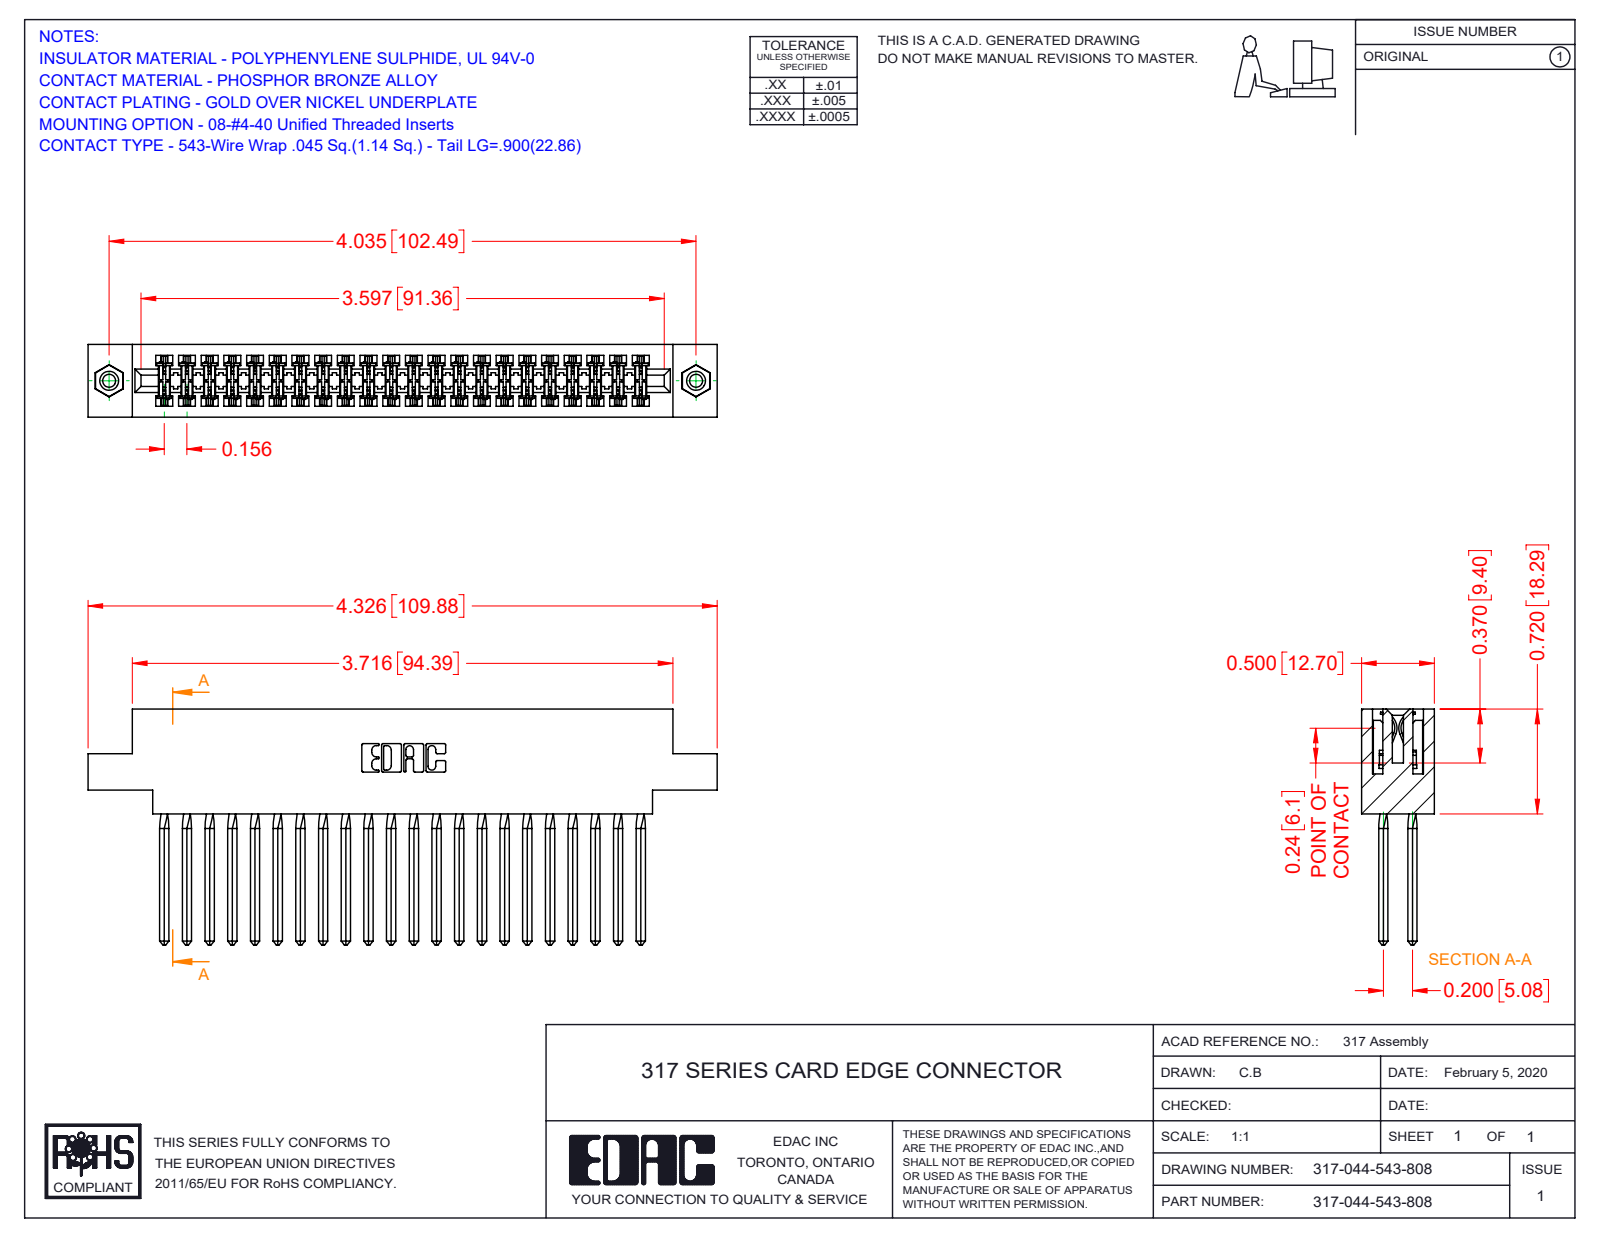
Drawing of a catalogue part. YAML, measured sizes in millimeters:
part_name: "317-290-001_543; 317-044-543-808; 345-250-001_345-250-003-102; 317 Part_.156 Dia - TI"
step_written_by: "SolidWorks 2016 (CONFIG_CONTROL_DESIGN)"
units: millimeters
bodies: {solids: 47, faces: 4078, planar: 3302, cylindrical: 584, other: 192}
overall_size: [109.9, 41.1, 12.7]
volume: 17980
surface_area: 26510
round_holes:
  - {diameter: 2.3, count: 2}
  - {diameter: 3.2, count: 2}
  - {diameter: 4, count: 2}
round_bosses_or_shafts:
  - {diameter: 3.9, count: 2}
partial_cylinders:
  - {radius: 0.4, count: 88}
  - {radius: 0.3, count: 22}
  - {radius: 0.2, count: 6}
  - {radius: 0.8, count: 6}
  - {radius: 0.7, count: 3}
  - {radius: 2.4, count: 2}
  - {radius: 2.5, count: 2}
  - {radius: 2.8, count: 2}
face_to_face_distances: [12.7, 1.9, 10.8, 2.8, 8.9, 5.6, 5, 18.3, 2.4, 5.1]
hole_center_spacings: [102.5]
